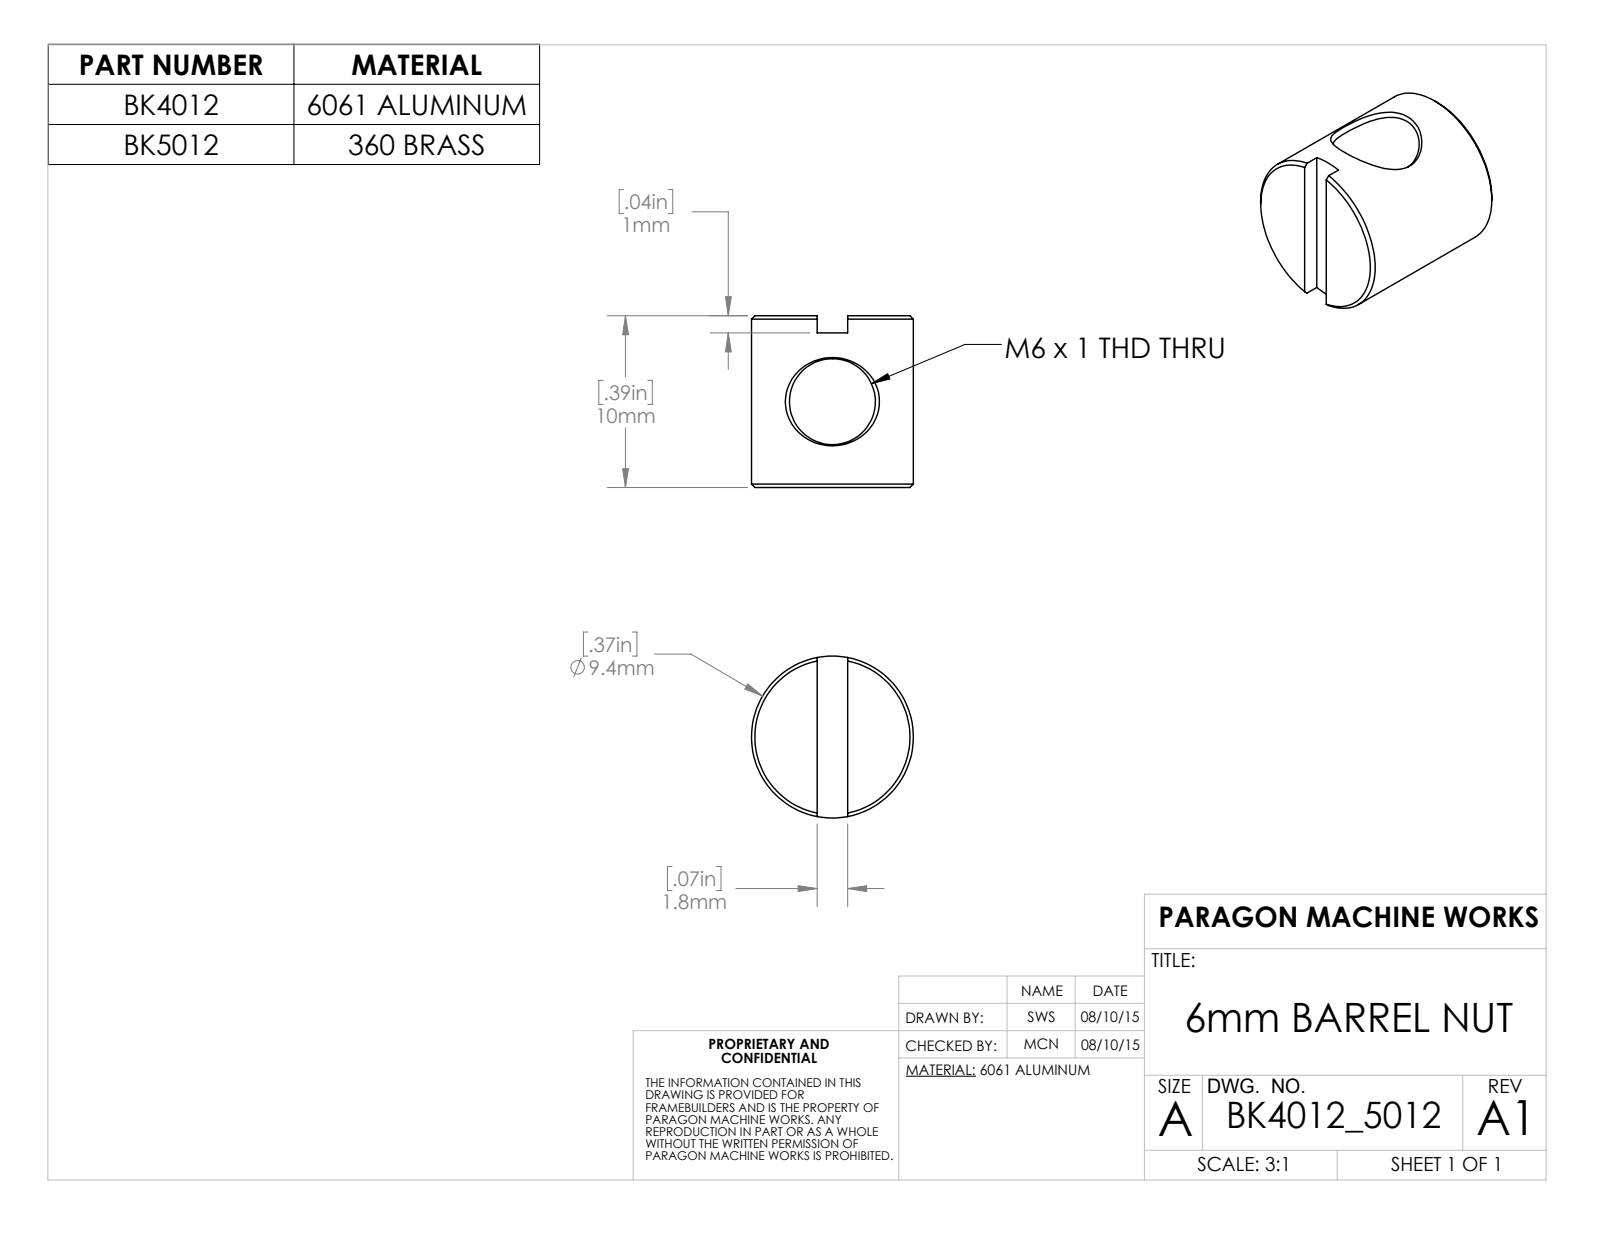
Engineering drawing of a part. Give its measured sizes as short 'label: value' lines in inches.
name: BK4012_5012
written by: SolidWorks 2023 (AUTOMOTIVE_DESIGN)
unit: in
bodies: 1 solid, 19 faces (6 planar, 4 cylindrical, 9 other)
size: 0.394 × 0.371 × 0.371
volume: 0.031 in³; area: 0.828 in²
holes: 1× ⌀0.197
bosses: 1× ⌀0.371
face distances: 0.394, 0.354, 0.039, 0.07
